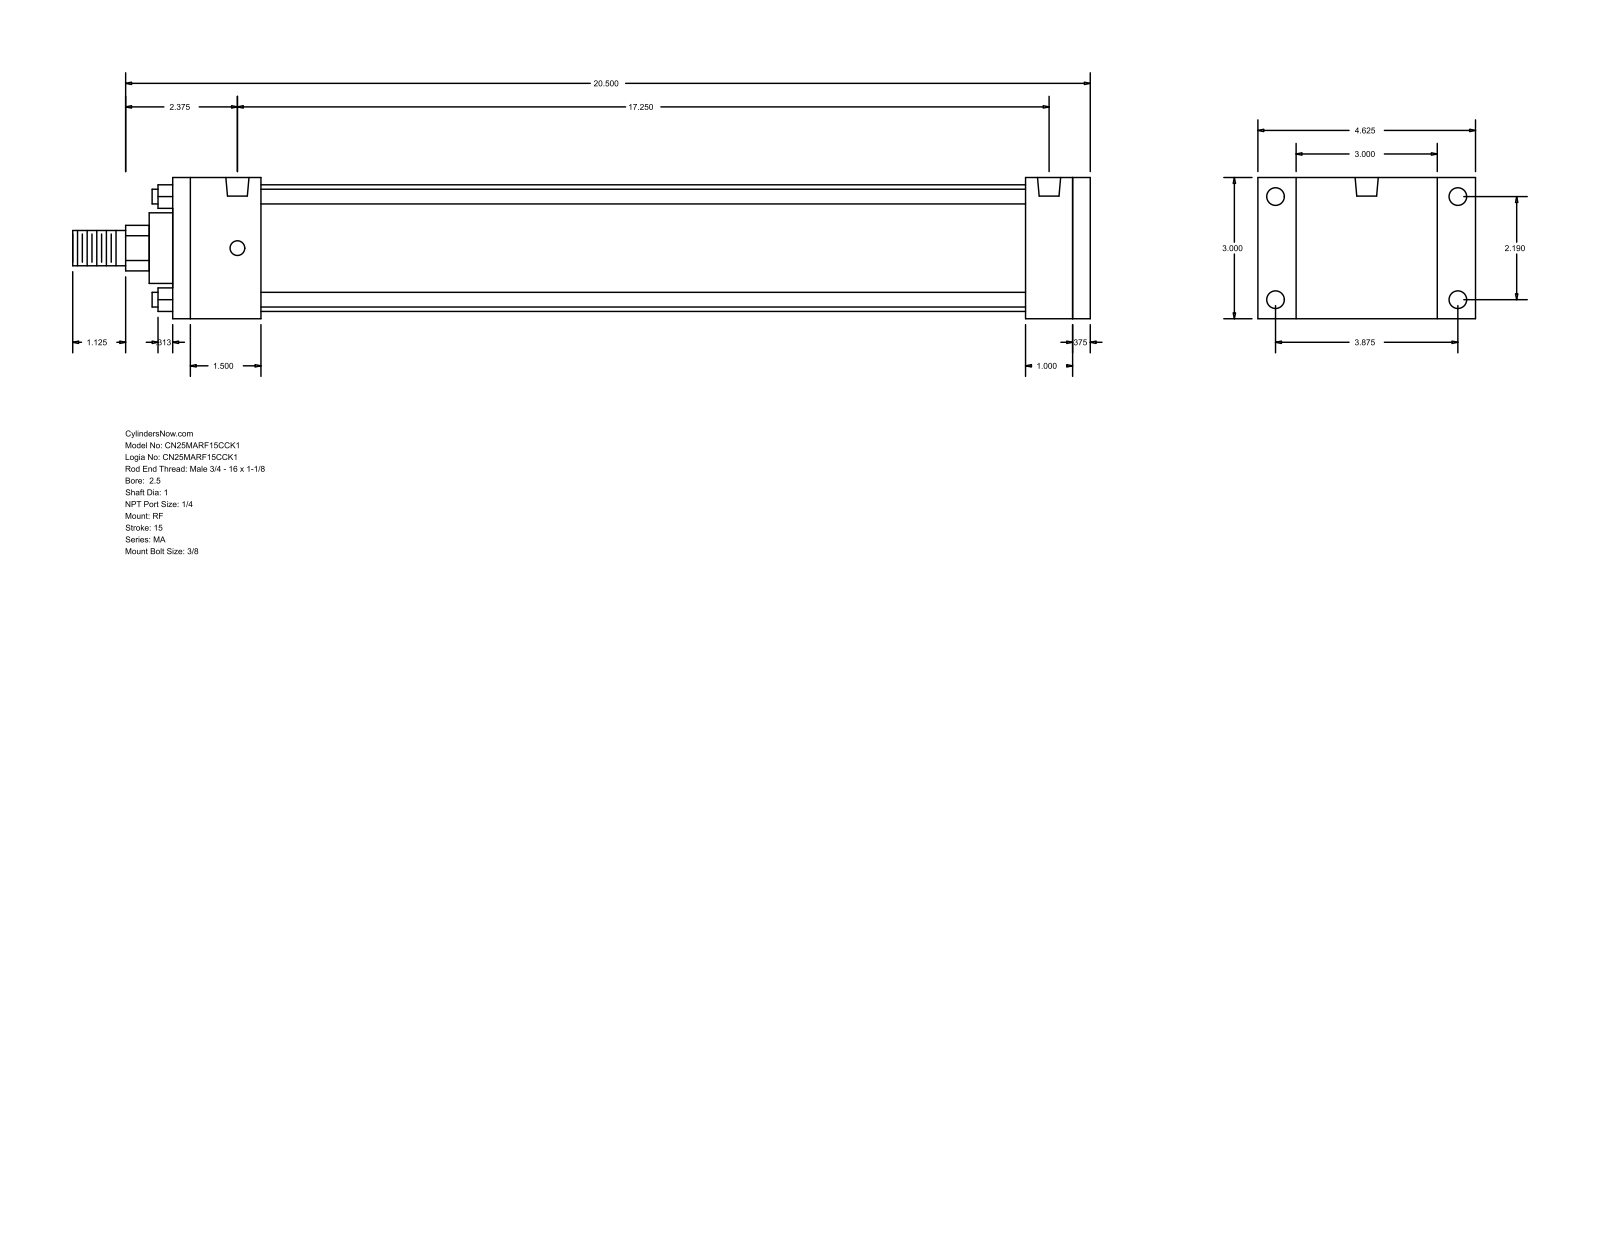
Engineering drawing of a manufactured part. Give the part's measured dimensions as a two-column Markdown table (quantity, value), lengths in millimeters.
| quantity | value |
| --- | --- |
| part name | MA_RF__0250_1 |
| STEP written by | GSSL Pune (CONFIG_CONTROL_DESIGN) |
| units | millimeters |
| bodies | 0 solids, 92 faces (64 planar, 28 cylindrical, 0 other) |
| overall size | 549.27 × 117.47 × 76.2 |
| round holes (diameter × count) | 7.94 × 4, 9.53 × 4, 12.49 × 2 |
| round bosses / shafts (diameter × count) | 7.94 × 4, 68.33 × 1, 38.1 × 1, 25.4 × 1, 19.05 × 1 |
| partial cylindrical surfaces (radius × count) | 12.29 × 1 |
| main face-to-face distances | 76.2, 495.3, 485.78, 9.52, 47.63, 460.37, 412.74, 438.15, 447.67, 25.41 |
| hole center spacings | 55.62, 98.42, 113.05, 438.15 |
